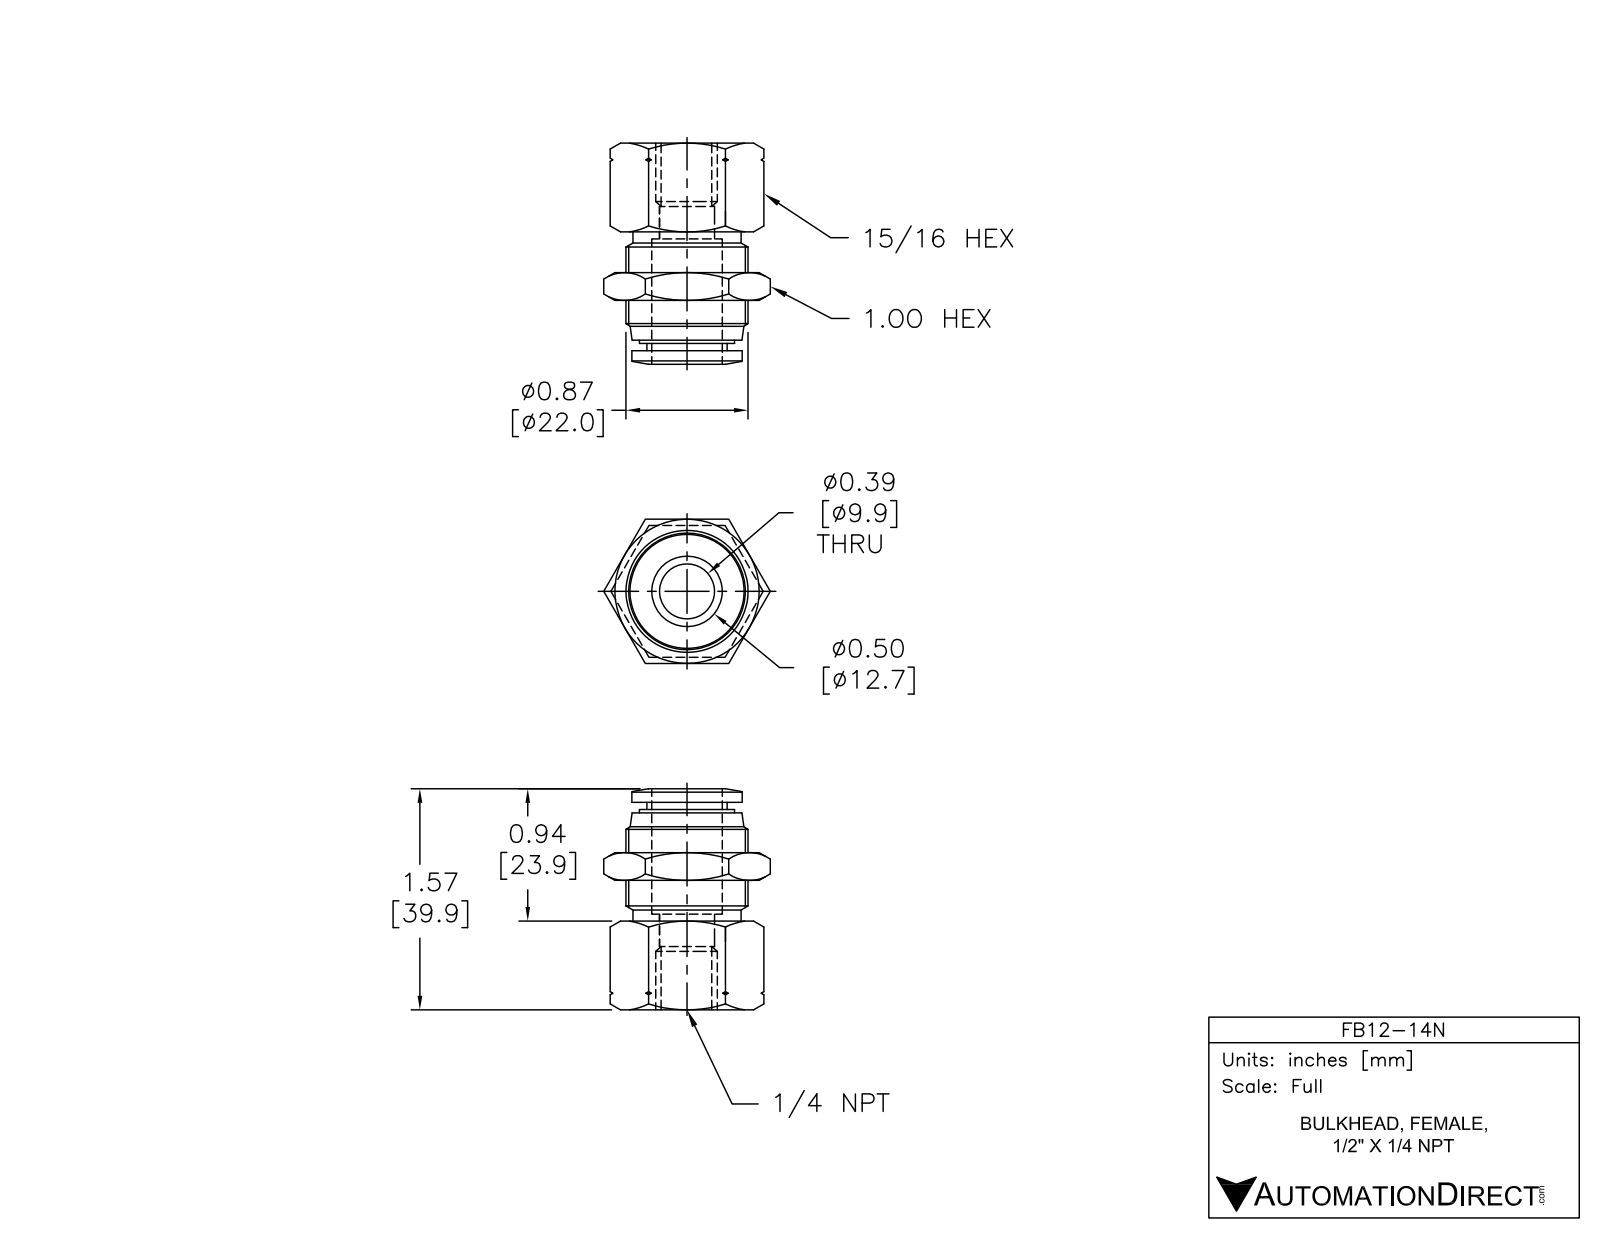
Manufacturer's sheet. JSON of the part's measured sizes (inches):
{"part_name": "FB12-14N", "step_written_by": "SolidWorks 2015 (AUTOMOTIVE_DESIGN)", "units": "inches", "bodies": {"solids": 1, "faces": 95, "planar": 21, "cylindrical": 16, "other": 58}, "overall_size": [1.569, 1.182, 1.024], "volume_in3": 0.725, "surface_area_in2": 9.465, "round_holes": [[0.394, 1], [0.51, 1]], "round_bosses_or_shafts": [[0.866, 1], [0.783, 1], [0.709, 1], [0.675, 1], [0.569, 1]], "face_to_face_distances": [0.945, 0.039, 0.984, 0.63, 1.024, 0.919, 0.289, 1.115, 0.485, 0.197]}
